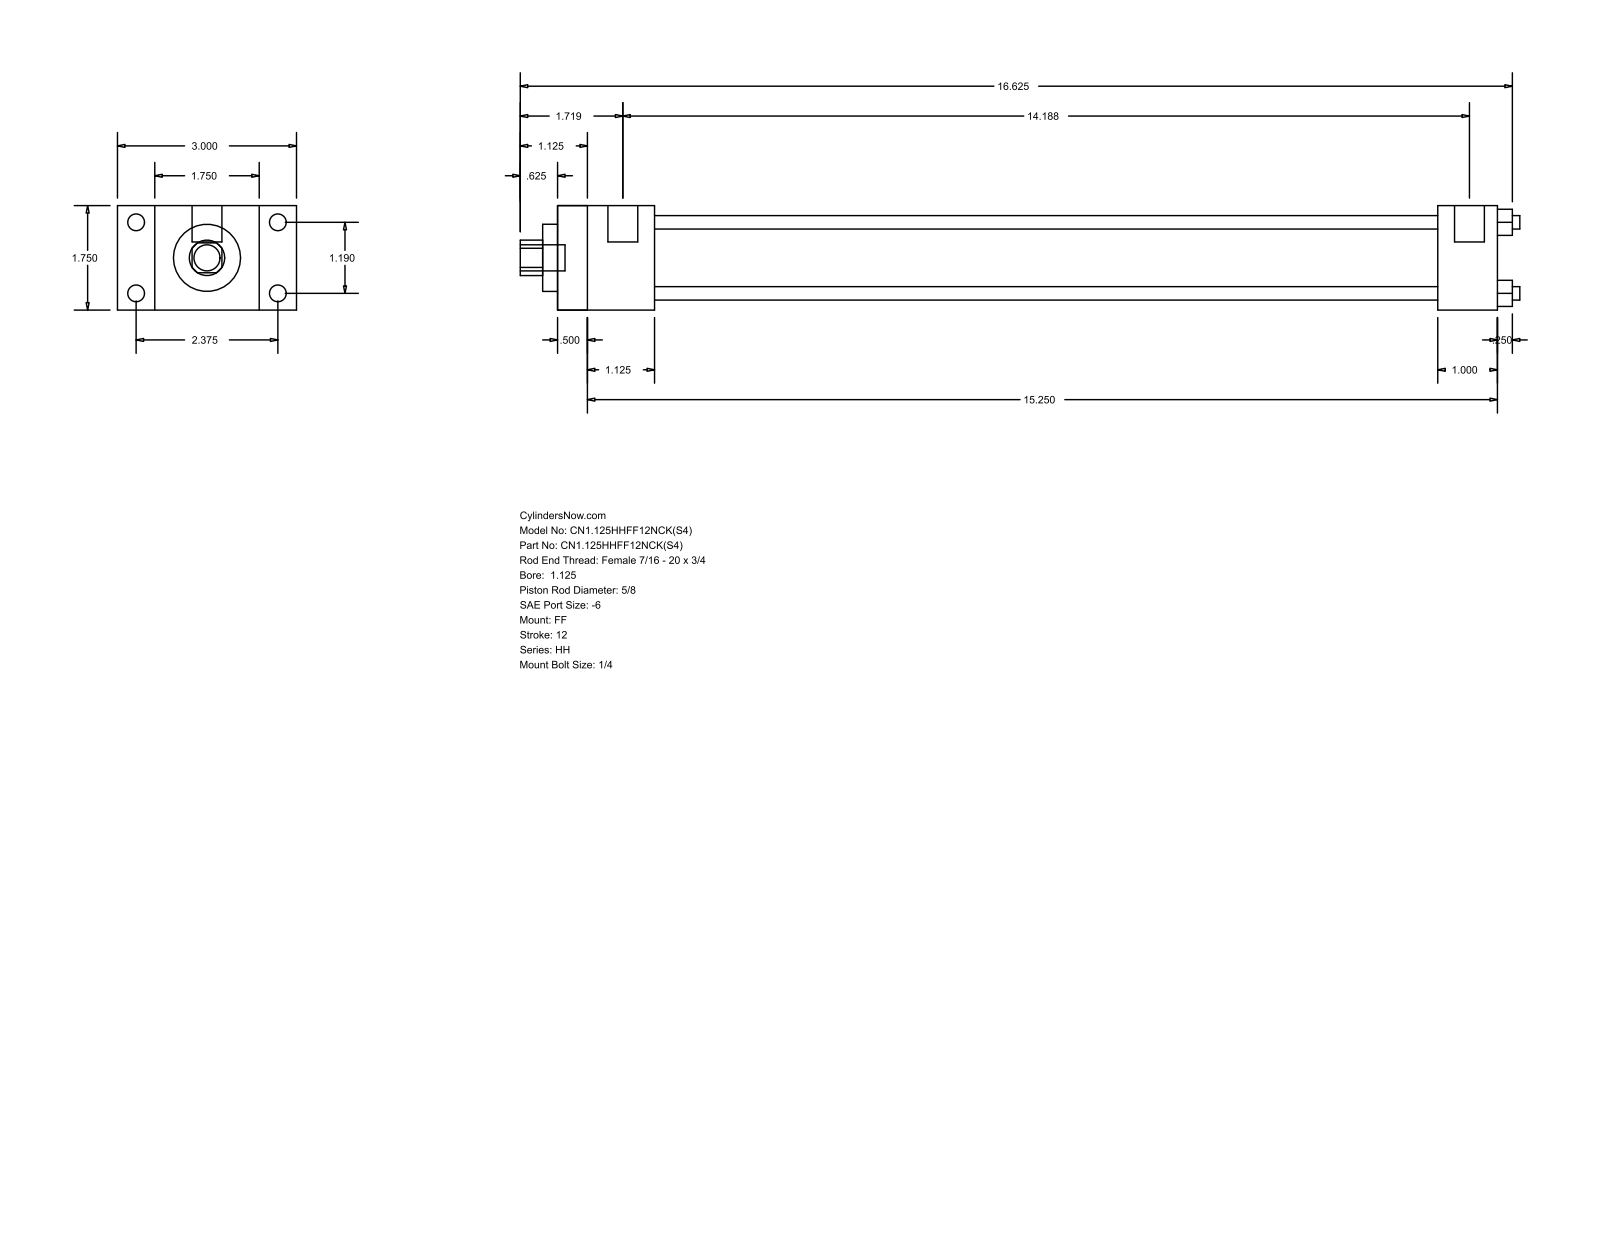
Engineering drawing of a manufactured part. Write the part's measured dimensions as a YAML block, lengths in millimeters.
part_name: "HH_FF__0112_0.625"
step_written_by: "GSSL Pune (CONFIG_CONTROL_DESIGN)"
units: millimeters
bodies: {solids: 0, faces: 92, planar: 64, cylindrical: 28, other: 0}
overall_size: [425.45, 76.2, 44.45]
round_holes:
  - {diameter: 5.71, count: 4}
  - {diameter: 15.88, count: 1}
  - {diameter: 28.57, count: 1}
  - {diameter: 34.92, count: 1}
round_bosses_or_shafts:
  - {diameter: 7.14, count: 4}
  - {diameter: 5.56, count: 4}
  - {diameter: 12.7, count: 2}
  - {diameter: 11.11, count: 1}
partial_cylinders:
  - {radius: 7.54, count: 1}
face_to_face_distances: [44.46, 400.05, 15.87, 12.69, 387.36, 60.33, 28.58, 41.27, 374.64, 361.95]
hole_center_spacings: [21.37, 30.22, 42.74]
